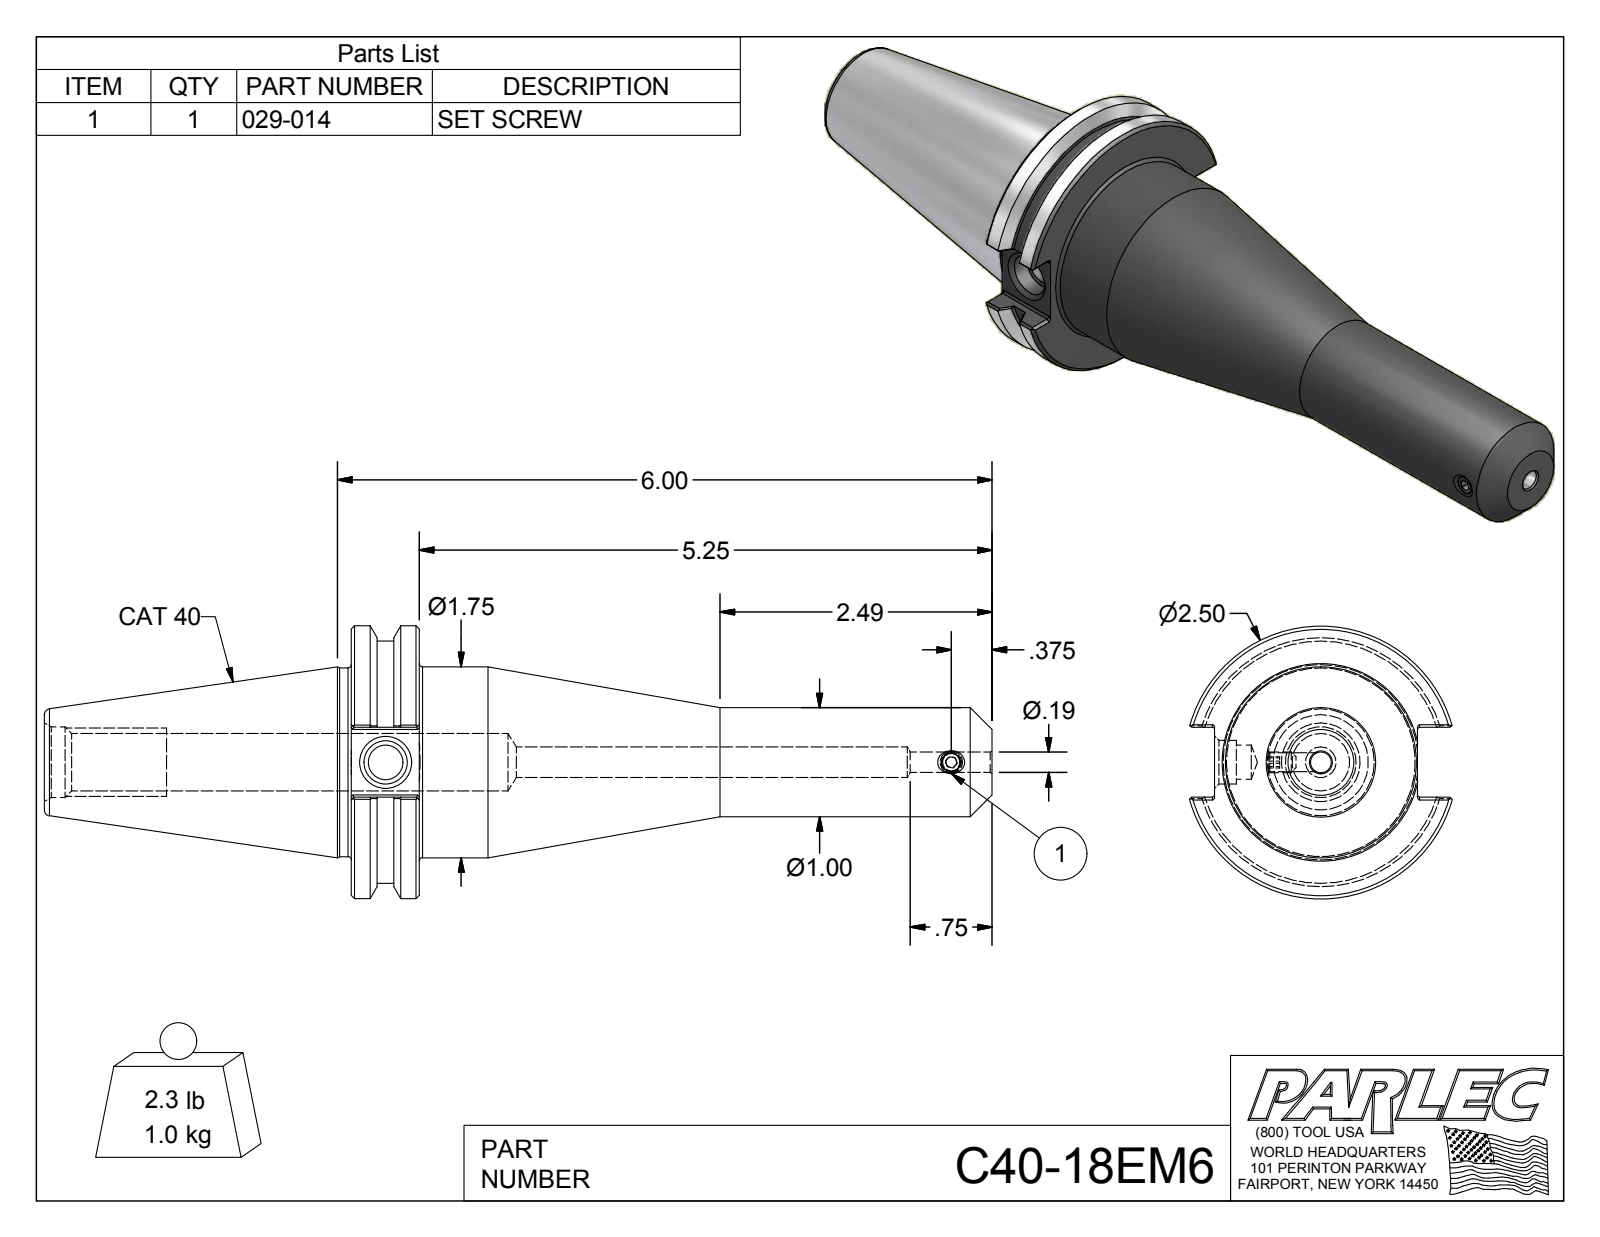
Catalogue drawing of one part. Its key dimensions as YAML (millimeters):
part_name: "C40-18EM6; C40-18EM6-1; 029-014"
step_written_by: "Autodesk Inventor 2012 (AUTOMOTIVE_DESIGN)"
units: millimeters
bodies: {solids: 2, faces: 102, planar: 40, cylindrical: 29, other: 33}
overall_size: [220.6, 63.5, 61.1]
volume: 202400
surface_area: 35830
round_holes:
  - {diameter: 4.4, count: 1}
  - {diameter: 4.7, count: 1}
  - {diameter: 7.1, count: 1}
  - {diameter: 8, count: 1}
  - {diameter: 10.1, count: 1}
  - {diameter: 13.4, count: 1}
  - {diameter: 16.5, count: 1}
round_bosses_or_shafts:
  - {diameter: 63.5, count: 1}
  - {diameter: 56.4, count: 1}
  - {diameter: 44.5, count: 1}
  - {diameter: 43.9, count: 1}
  - {diameter: 25.4, count: 1}
  - {diameter: 4.8, count: 1}
partial_cylinders:
  - {radius: 0.5, count: 12}
face_to_face_distances: [15.9, 149.2, 133.4, 16.3, 47.2, 71.4, 87.3, 220.6, 81.3, 9.9]
hole_center_spacings: [131.7]
